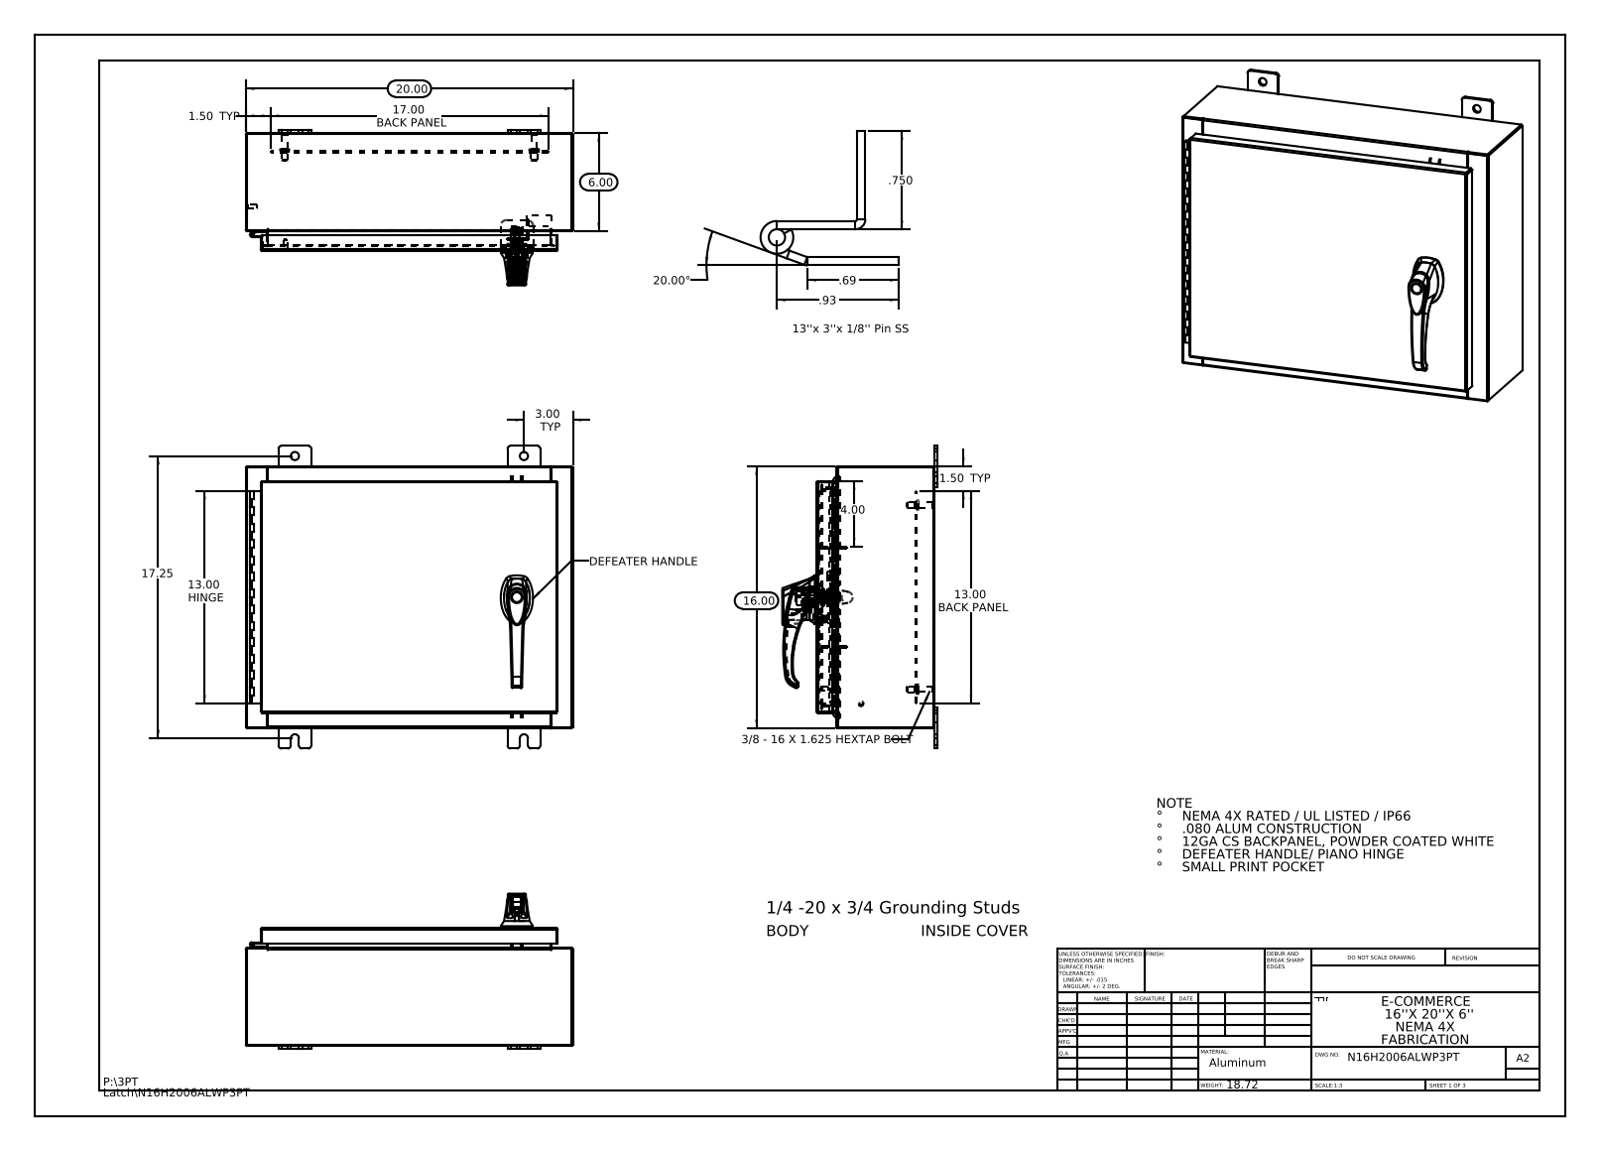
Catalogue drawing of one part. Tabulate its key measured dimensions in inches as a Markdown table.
| quantity | value |
| --- | --- |
| part name | N16H2006ALWP3PT Defeater Handle Rod; g26103103_26163303; N16H2006ALWP3PT Cover; N16H2006ALWP3PT Hinge Enclosure Side2 (+8 more) |
| STEP written by | SolidWorks 2013 (CONFIG_CONTROL_DESIGN) |
| units | inches |
| bodies | 37 solids, 2290 faces (775 planar, 817 cylindrical, 698 other) |
| overall size | 20 × 18.5 × 9.495 |
| volume | 128.6 in³ |
| surface area | 3 157 in² |
| round holes (diameter × count) | 0.5 × 8, 0.25 × 4, 0.138 × 3, 0.161 × 3, 0.079 × 2, 0.203 × 2, 0.313 × 2, 0.437 × 2, 0.125 × 1, 0.125 × 1, 0.197 × 1, 0.276 × 1 |
| round bosses / shafts (diameter × count) | 0.625 × 4, 0.375 × 4, 0.33 × 4, 0.157 × 4, 0.14 × 4, 0.315 × 3, 0.236 × 3, 1.181 × 1 |
| partial cylindrical surfaces (radius × count) | 0.118 × 37, 0.006 × 33, 0.19 × 24, 0.013 × 20, 0.088 × 18, 0.039 × 15, 0.028 × 12, 0.008 × 6 |
| main face-to-face distances | 0.075, 7.126, 7.051, 7.201, 15.925, 1, 0.104, 1.075, 6.051, 6.126 |
| hole center spacings | 3.708, 0.295, 0.625, 0.841, 1.25, 1.313, 1.32, 1.484 |
